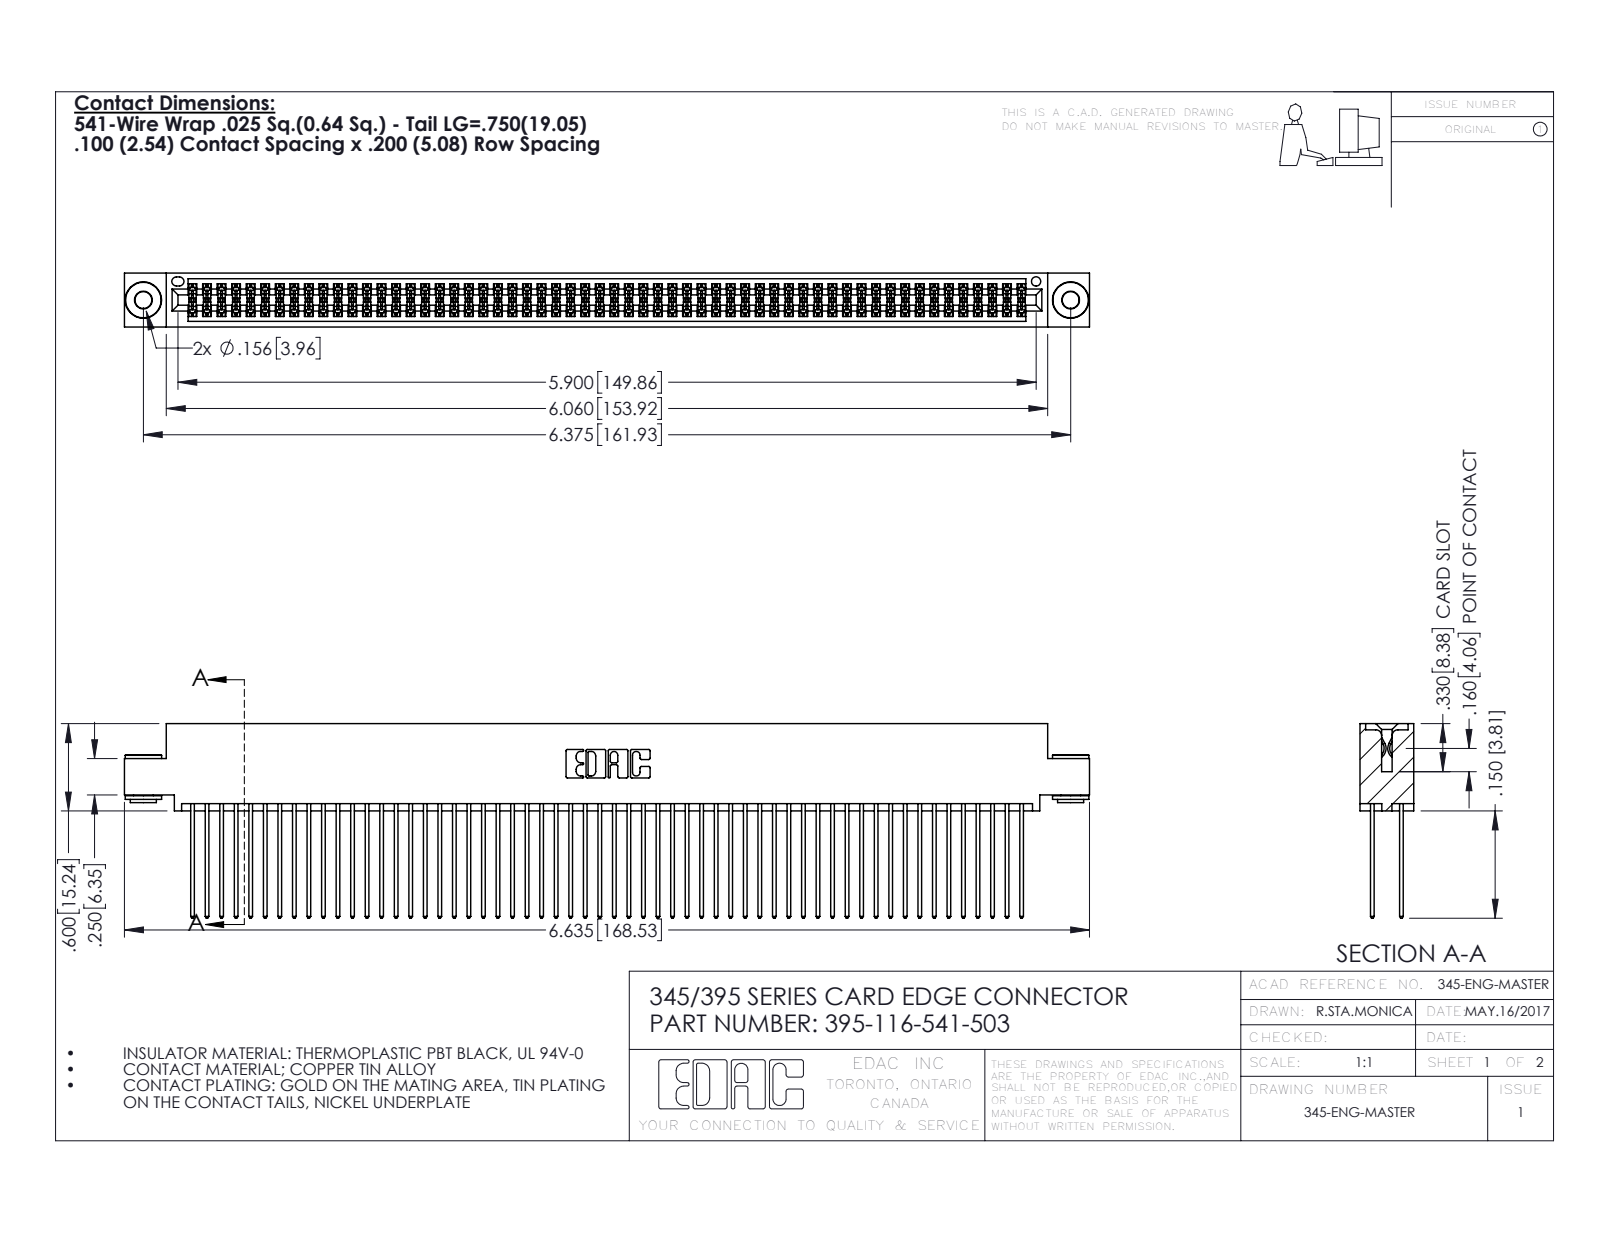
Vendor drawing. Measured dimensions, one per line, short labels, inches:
name: 395-116-541-503; 345-250-002_345-250-002-102; 345 Part_0.110 Offset - 0.156 Dia-TH; 345-292-001_345-293-141
written by: SolidWorks 2016 (CONFIG_CONTROL_DESIGN)
unit: in
bodies: 119 solids, 5968 faces (3922 planar, 2038 cylindrical, 8 other)
size: 6.635 × 1.337 × 0.37
volume: 1.045 in³; area: 45.04 in²
holes: 2× ⌀0.116, 2× ⌀0.156, 1× ⌀0.064
bosses: 2× ⌀0.25, 2× ⌀0.18, 2× ⌀0.136
rounds: 174× R0.006, 116× R0.01, 22× R0.01, 6× R0.007, 6× R0.031, 3× R0.026, 2× R0.014, 2× R0.019
face distances: 0.072, 0.298, 0.2, 0.025, 0.098, 0.272, 0.225, 0.37, 0.175, 0.149
hole spacings: 0.27, 6.139, 6.375
